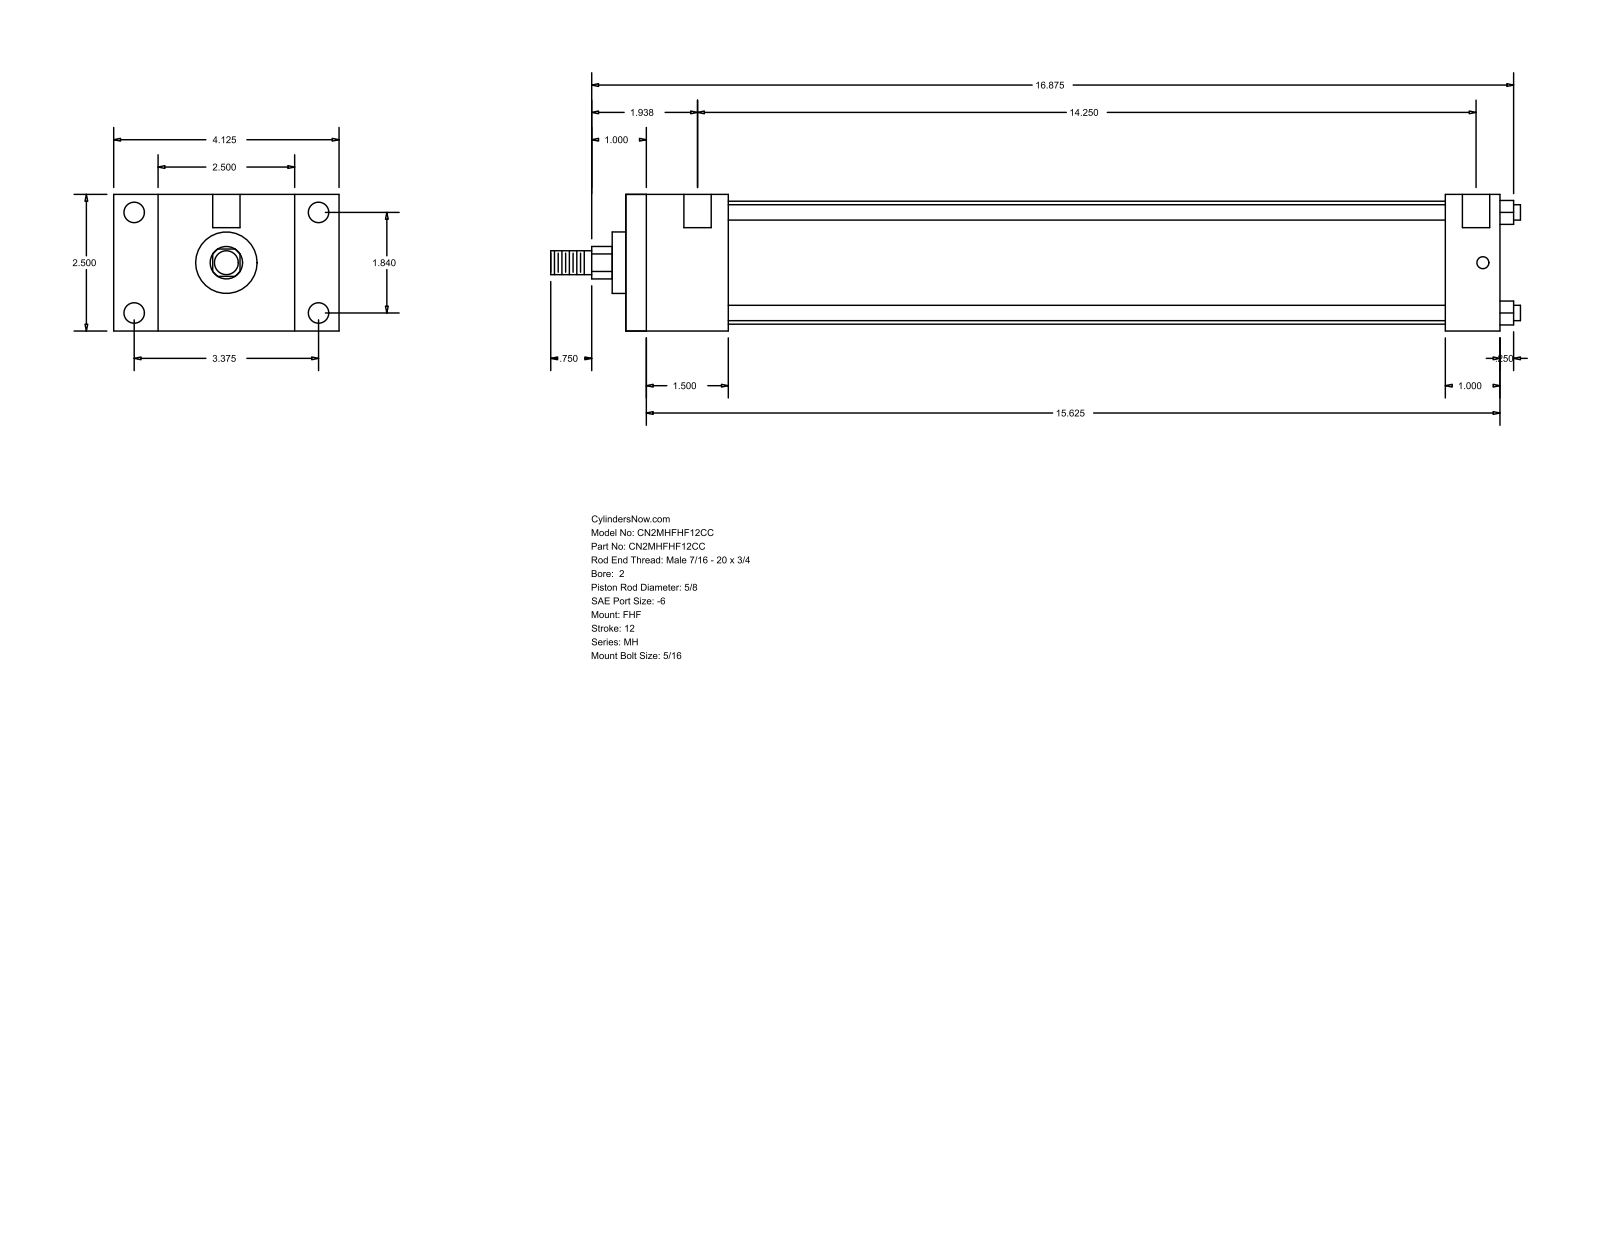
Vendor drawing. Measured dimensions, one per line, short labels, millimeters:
name: MH_FHF__0200_0.625
written by: GSSL Pune (CONFIG_CONTROL_DESIGN)
unit: mm
bodies: 0 solids, 88 faces (60 planar, 28 cylindrical, 0 other)
size: 450.85 × 104.78 × 63.5
holes: 4× ⌀5.56, 4× ⌀9.53, 2× ⌀12.7
bosses: 4× ⌀7.14, 1× ⌀57.15, 1× ⌀28.57, 1× ⌀15.88, 1× ⌀11.11
rounds: 1× R7.54
face distances: 63.5, 47.62, 406.39, 358.77, 20.64, 84.14, 104.78, 381, 333.38, 25.39
hole spacings: 46.74, 85.72, 97.63, 369.89, 3.18, 4.76, 361.95, 365.13
